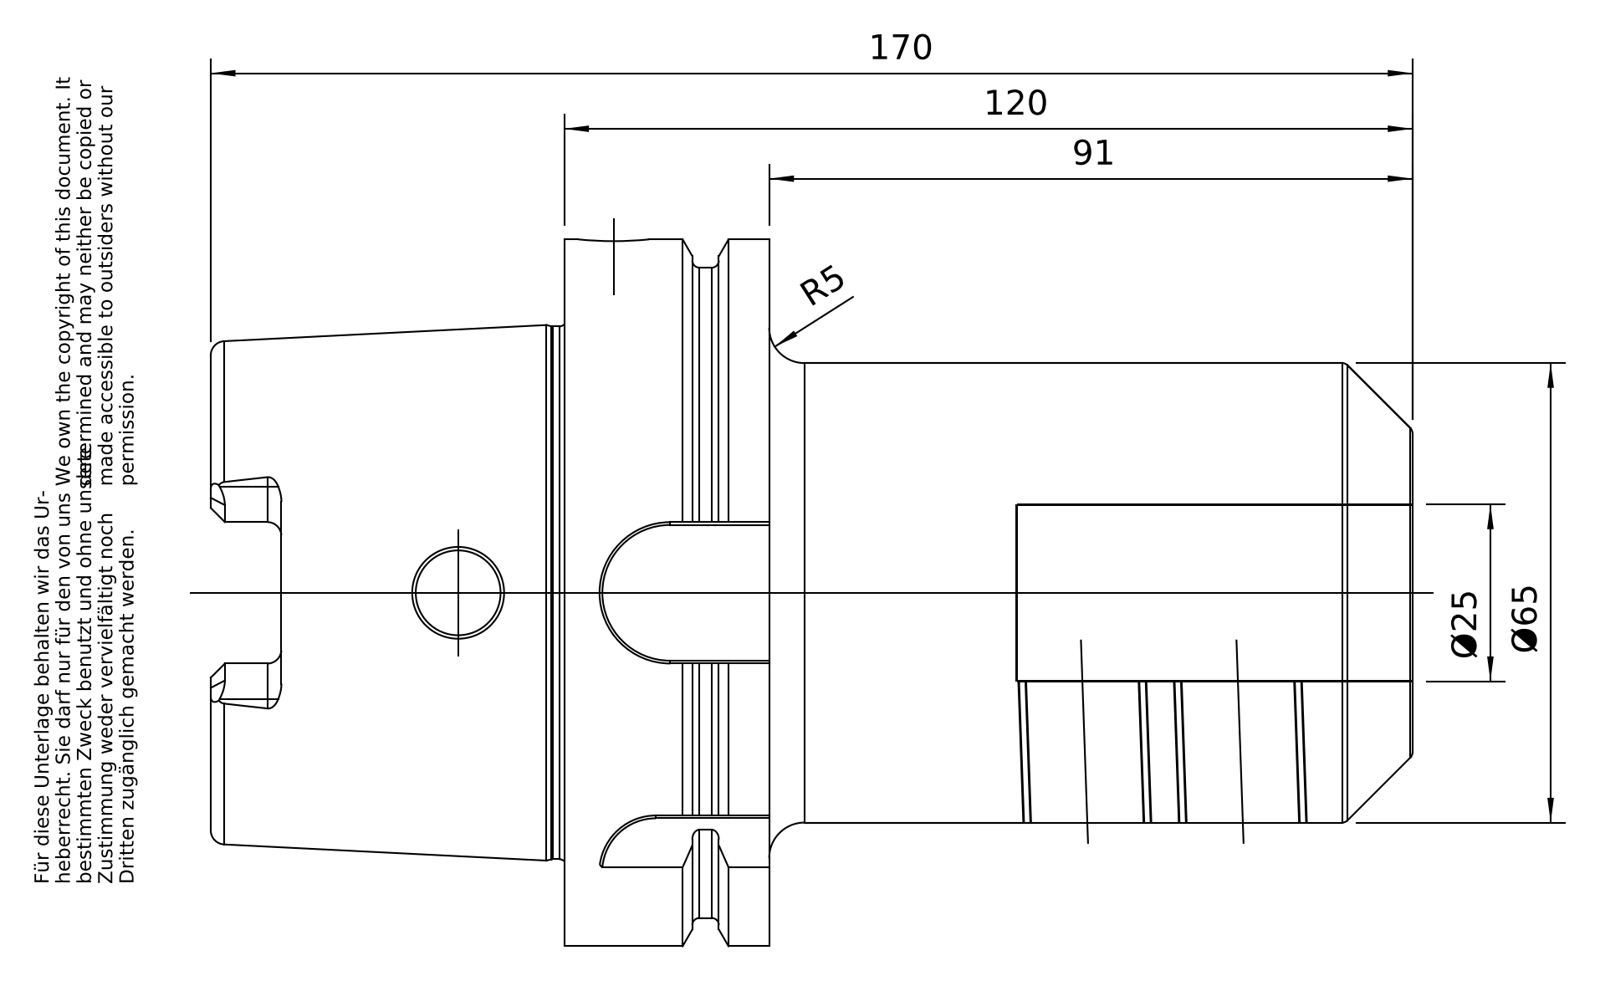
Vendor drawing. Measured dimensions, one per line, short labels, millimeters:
name: A100-030-25
written by: PRO/ENGINEER BY PARAMETRIC TECHNOLOGY CORPORATION, 2010430 (CONFIG_CONTROL_DESIGN)
unit: mm
bodies: 1 solid, 186 faces (51 planar, 60 cylindrical, 75 other)
size: 170 × 100 × 100
volume: 513 276 mm³; area: 75 197 mm²
holes: 2× ⌀16, 2× ⌀18, 1× ⌀10, 1× ⌀12, 1× ⌀22.5, 1× ⌀24, 1× ⌀24.32, 1× ⌀24.5, 1× ⌀25, 1× ⌀53, 1× ⌀63
bosses: 1× ⌀100, 1× ⌀92, 1× ⌀75.36, 1× ⌀65
rounds: 6× R2, 4× R5, 1× R8, 1× R10, 1× R11
face distances: 29, 12.5, 16.5, 120, 107.5, 91, 50, 62.5, 79, 170
hole spacings: 21.98
